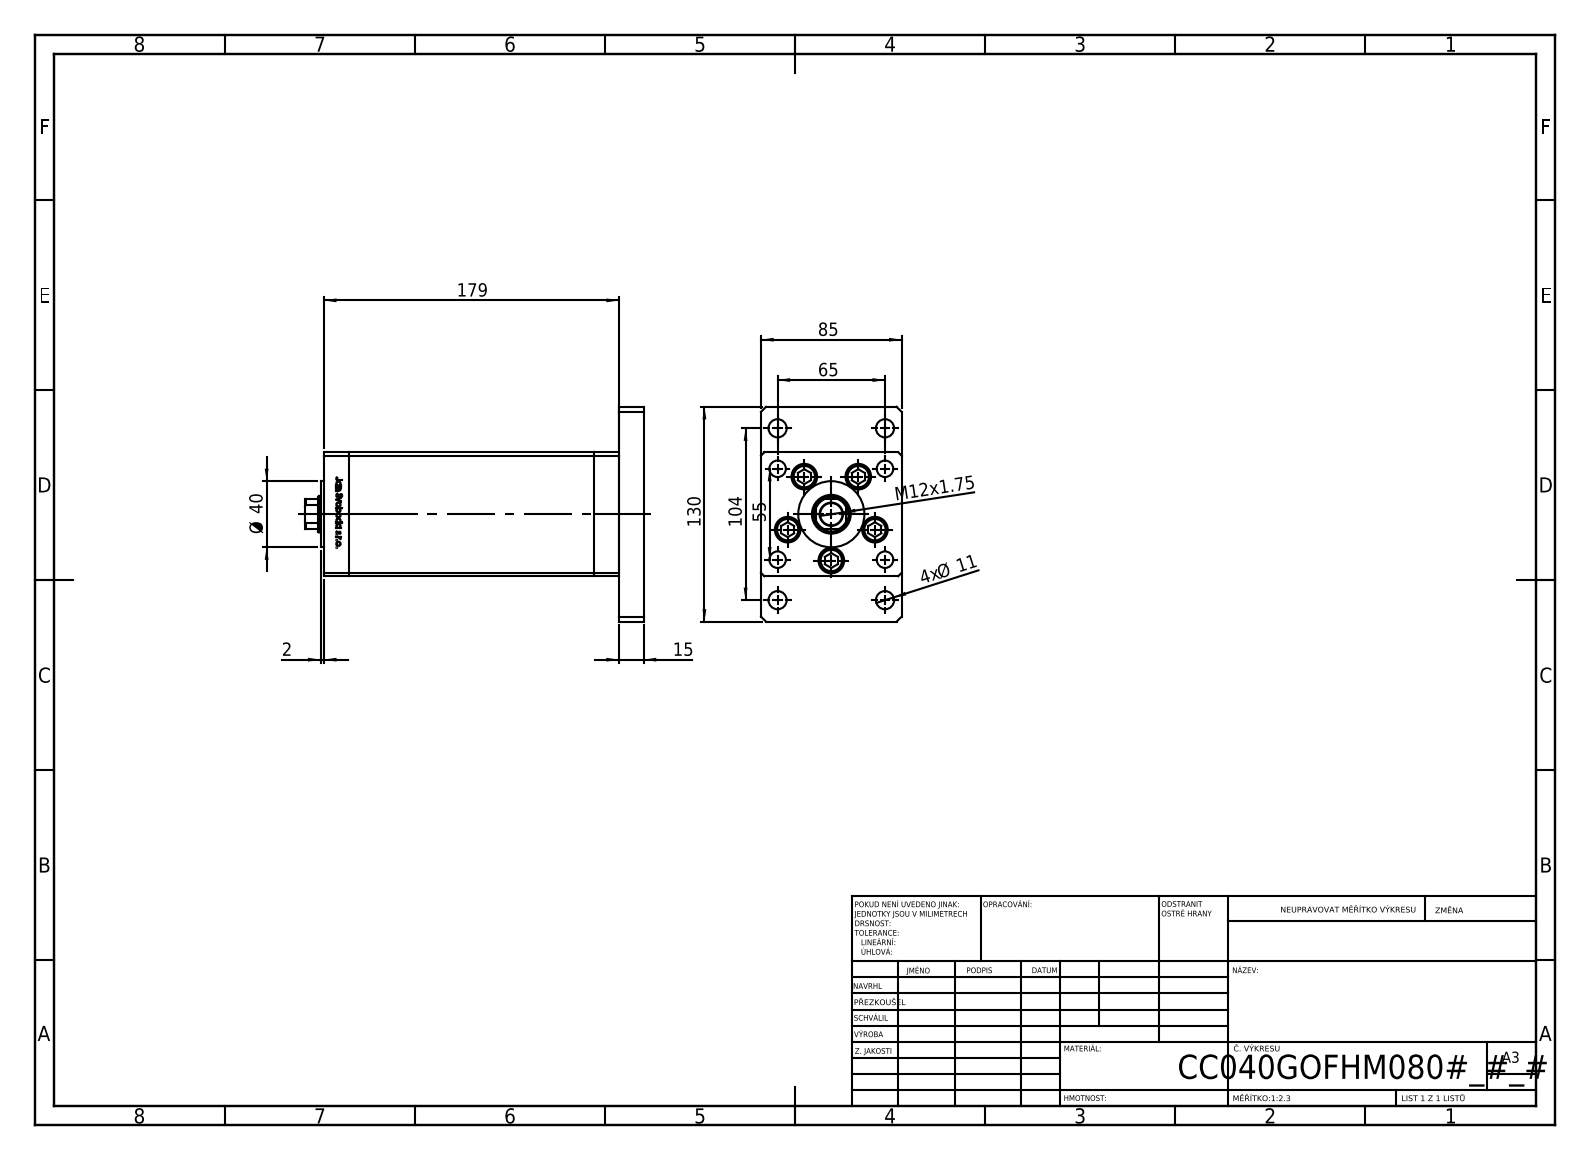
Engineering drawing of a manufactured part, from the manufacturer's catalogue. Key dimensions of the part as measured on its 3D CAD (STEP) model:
Part name (STEP PRODUCT): V220C_G_MIDDLE; ALLEN BOLT; V220C_FRONT_G; V220C BACK_G (+2 more)
STEP written by: SolidWorks 2019 (CONFIG_CONTROL_DESIGN)
Units: millimetres
Bodies: 19 solids, 1301 faces (514 planar, 181 cylindrical, 606 other)
Overall size (bounding box): 205 × 130 × 85
Volume: 1 162 000 mm³ · Surface area: 196 296 mm²
Round holes (diameter × count): ⌀10 ×9, ⌀11 ×9, ⌀15.5 ×5, ⌀14.5 ×4, ⌀13.5 ×1, ⌀22 ×1, ⌀23.5 ×1, ⌀56 ×1
Round bosses / shafts (diameter × count): ⌀8 ×9, ⌀14.5 ×5, ⌀40 ×1
Partial cylindrical surfaces — rounded edges, fillets, slot ends (radius × count): R0.93 ×2, R10.5 ×1
Main face-to-face distances: 15, 85, 163.5, 178.5, 75, 148.5, 30, 2, 176.5, 193.5
Hole centre spacings: 28, 24.5, 42.57, 61.32, 65, 69.46, 79.5, 102.69
